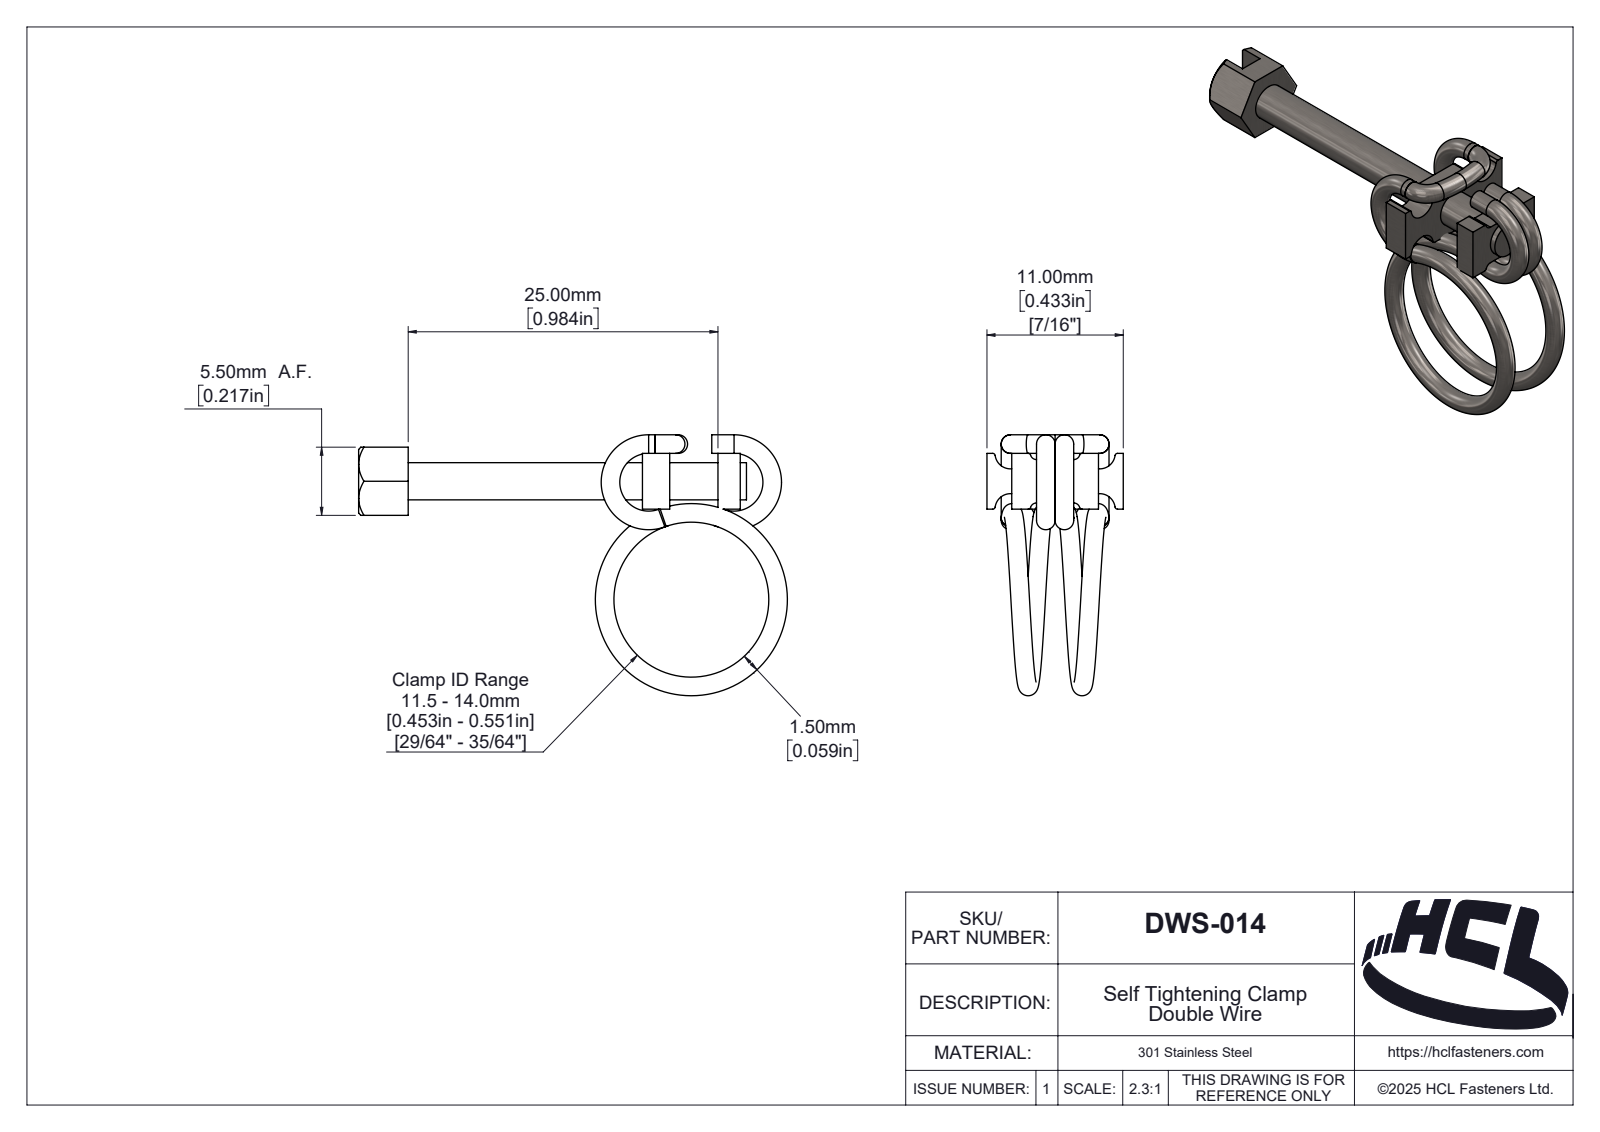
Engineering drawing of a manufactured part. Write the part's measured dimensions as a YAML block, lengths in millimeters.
part_name: "DWS-014"
step_written_by: "SolidWorks 2025 (AUTOMOTIVE_DESIGN)"
units: millimeters
bodies: {solids: 6, faces: 213, planar: 53, cylindrical: 74, other: 86}
overall_size: [34.6, 21.05, 11]
volume: 658
surface_area: 1404
round_holes:
  - {diameter: 3, count: 1}
round_bosses_or_shafts:
  - {diameter: 1.5, count: 4}
partial_cylinders:
  - {radius: 0.2, count: 12}
  - {radius: 0.5, count: 4}
  - {radius: 1.25, count: 4}
  - {radius: 0.4, count: 1}
  - {radius: 0.51, count: 1}
  - {radius: 0.53, count: 1}
  - {radius: 0.64, count: 1}
  - {radius: 0.91, count: 1}
face_to_face_distances: [4.5, 2, 0.5, 2.2, 5.49, 4, 6.1, 3.9, 7.9, 5.7]
